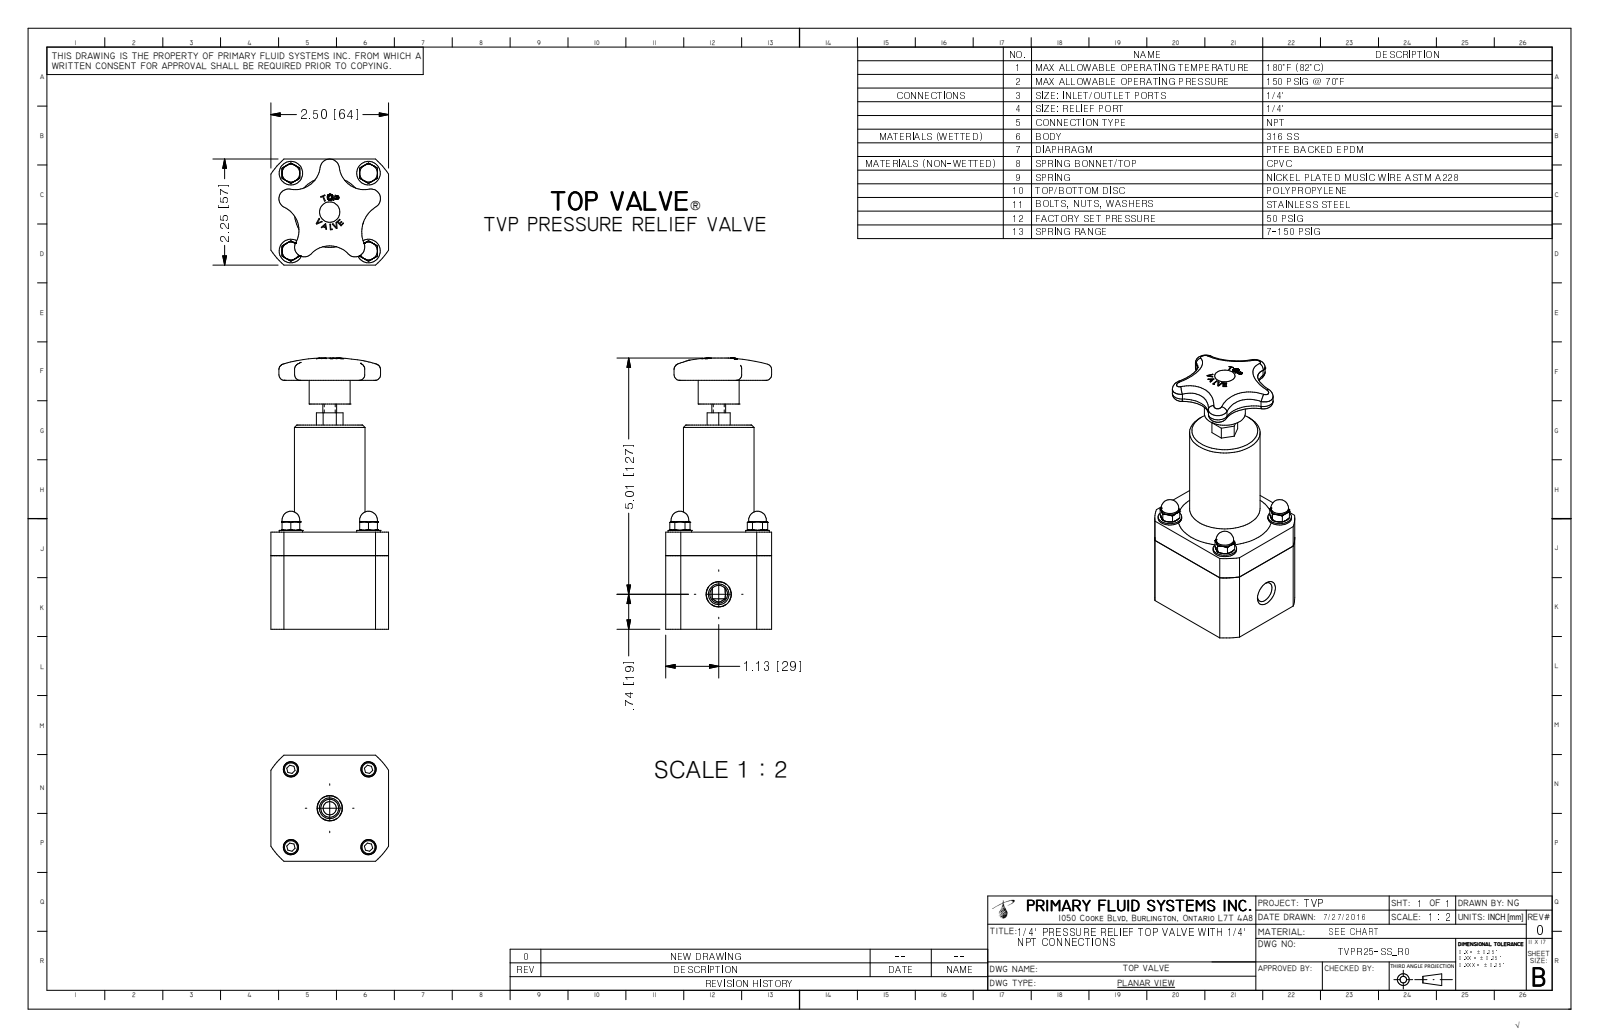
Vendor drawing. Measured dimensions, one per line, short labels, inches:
name: TVPR25-SS_R0
written by: Autodesk Inventor 2009 (AUTOMOTIVE_DESIGN)
unit: in
bodies: 1 solid, 356 faces (147 planar, 48 cylindrical, 161 other)
size: 5.75 × 2.5 × 2.25
volume: 16.4 in³; area: 56.45 in²
holes: 4× ⌀0.147, 2× ⌀0.437, 1× ⌀1.525
bosses: 4× ⌀0.5, 4× ⌀0.375, 4× ⌀0.312, 1× ⌀1.5, 1× ⌀0.87, 1× ⌀0.293
rounds: 5× R0.085, 5× R0.205, 4× R0.536, 4× R0.656, 1× R0.625, 1× R0.745, 1× R1.488
face distances: 2.25, 2.5, 2.06, 4.33, 2.27, 4.776, 2.716, 0.446, 2.096, 0.036
hole spacings: 1.167, 1.167, 1.65, 1.65, 2.334
